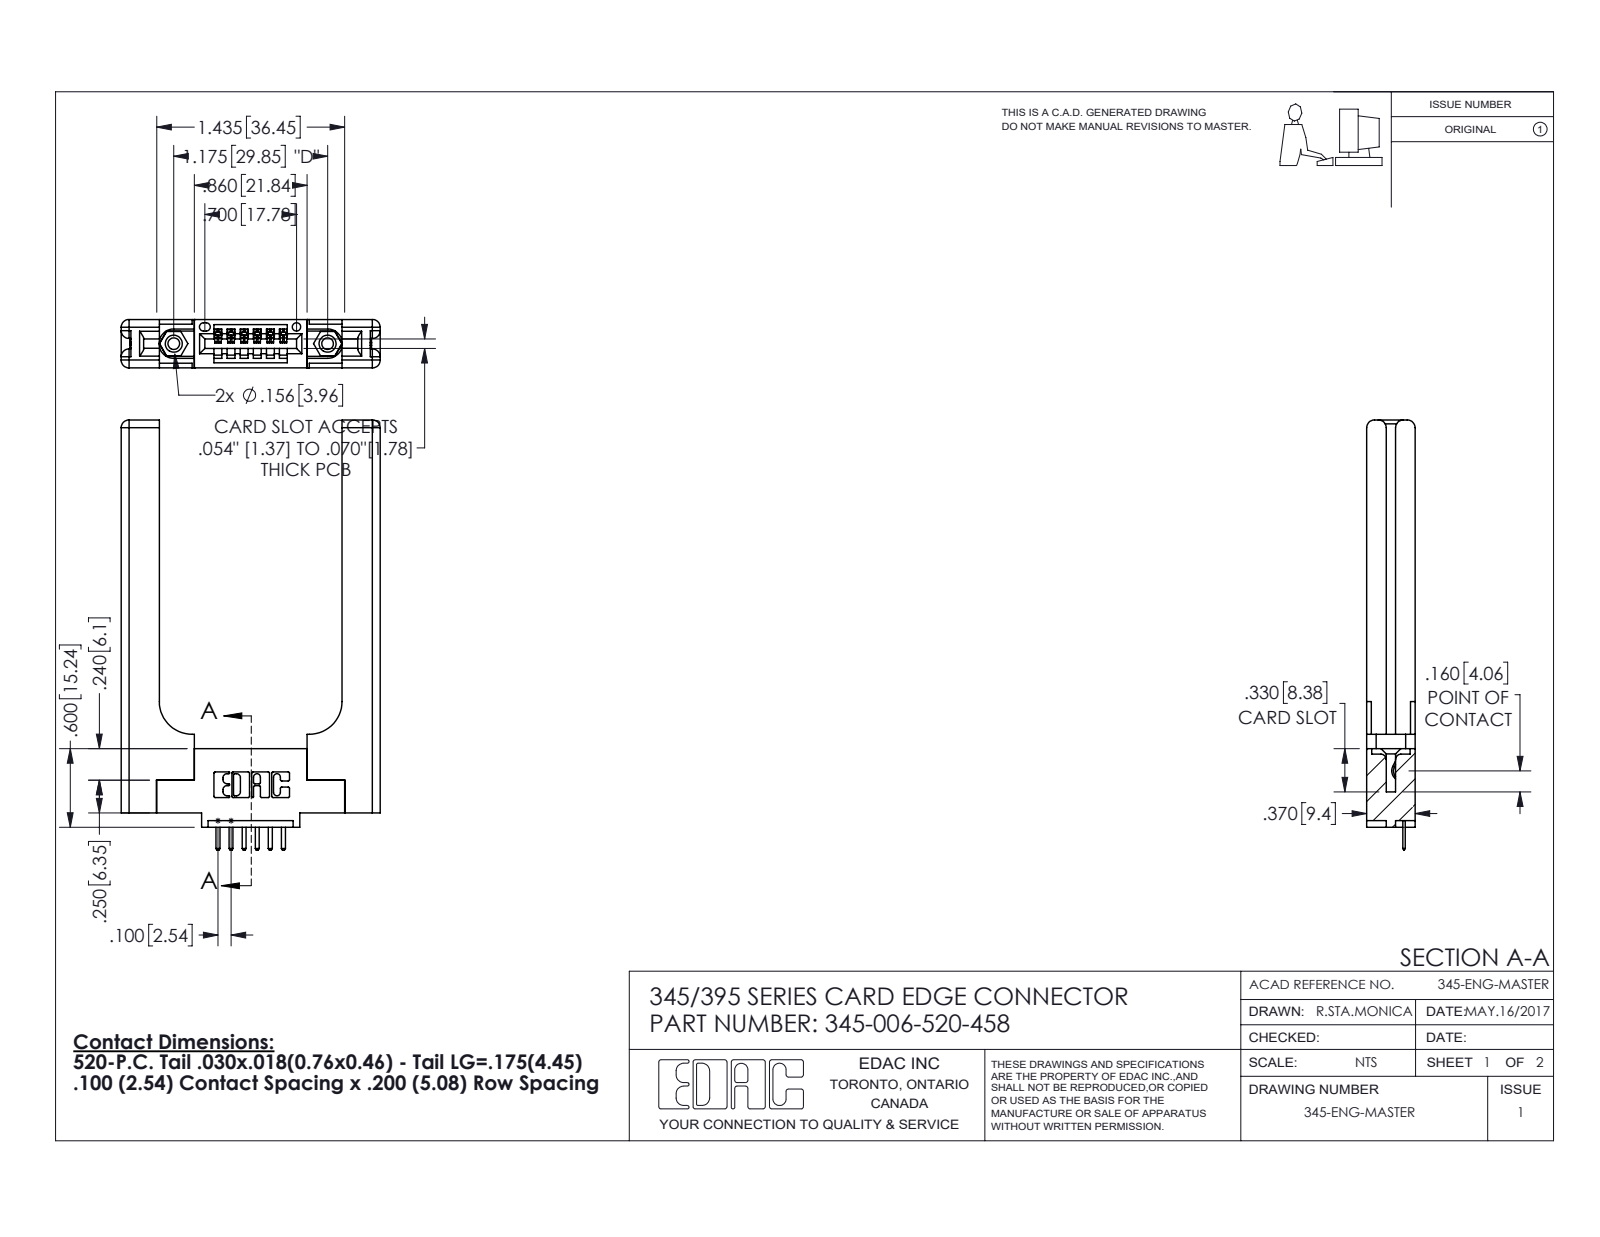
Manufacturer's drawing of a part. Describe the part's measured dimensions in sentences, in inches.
The part is named "345-292-001_345-293-120; 345 Part_0.110 Offset - 0.156 Dia-TH; 345-250-001_345-250-001-102; 345-220-058_345-220-058 (+1 more)". Its 3-D file was written by "SolidWorks 2016 (CONFIG_CONTROL_DESIGN)". It is 11 solids with 758 faces: 484 planar, 214 cylindrical and 60 other. Overall it measures 3.285 by 1.979 by 0.37 inches. Its volume is 0.787 cubic inches and its surface area 16.54 square inches. Round holes: 2 of diameter 0.089, 2 of diameter 0.125, 2 of diameter 0.156, 1 of diameter 0.064. Round bosses or shafts: 2 of diameter 0.155. Partial cylindrical surfaces (rounded edges, fillets, slot ends): 22 of radius 0.01, 16 of radius 0.06, 14 of radius 0.01, 12 of radius 0.006, 6 of radius 0.007, 6 of radius 0.031, 3 of radius 0.026, 2 of radius 0.03. The main face-to-face distances are 0.37, 0.15, 0.22, 0.072, 1.396, 0.077, 0.148, 0.071, 0.298, 0.292. The hole center spacings are 0.27, 0.946, 1.175.
